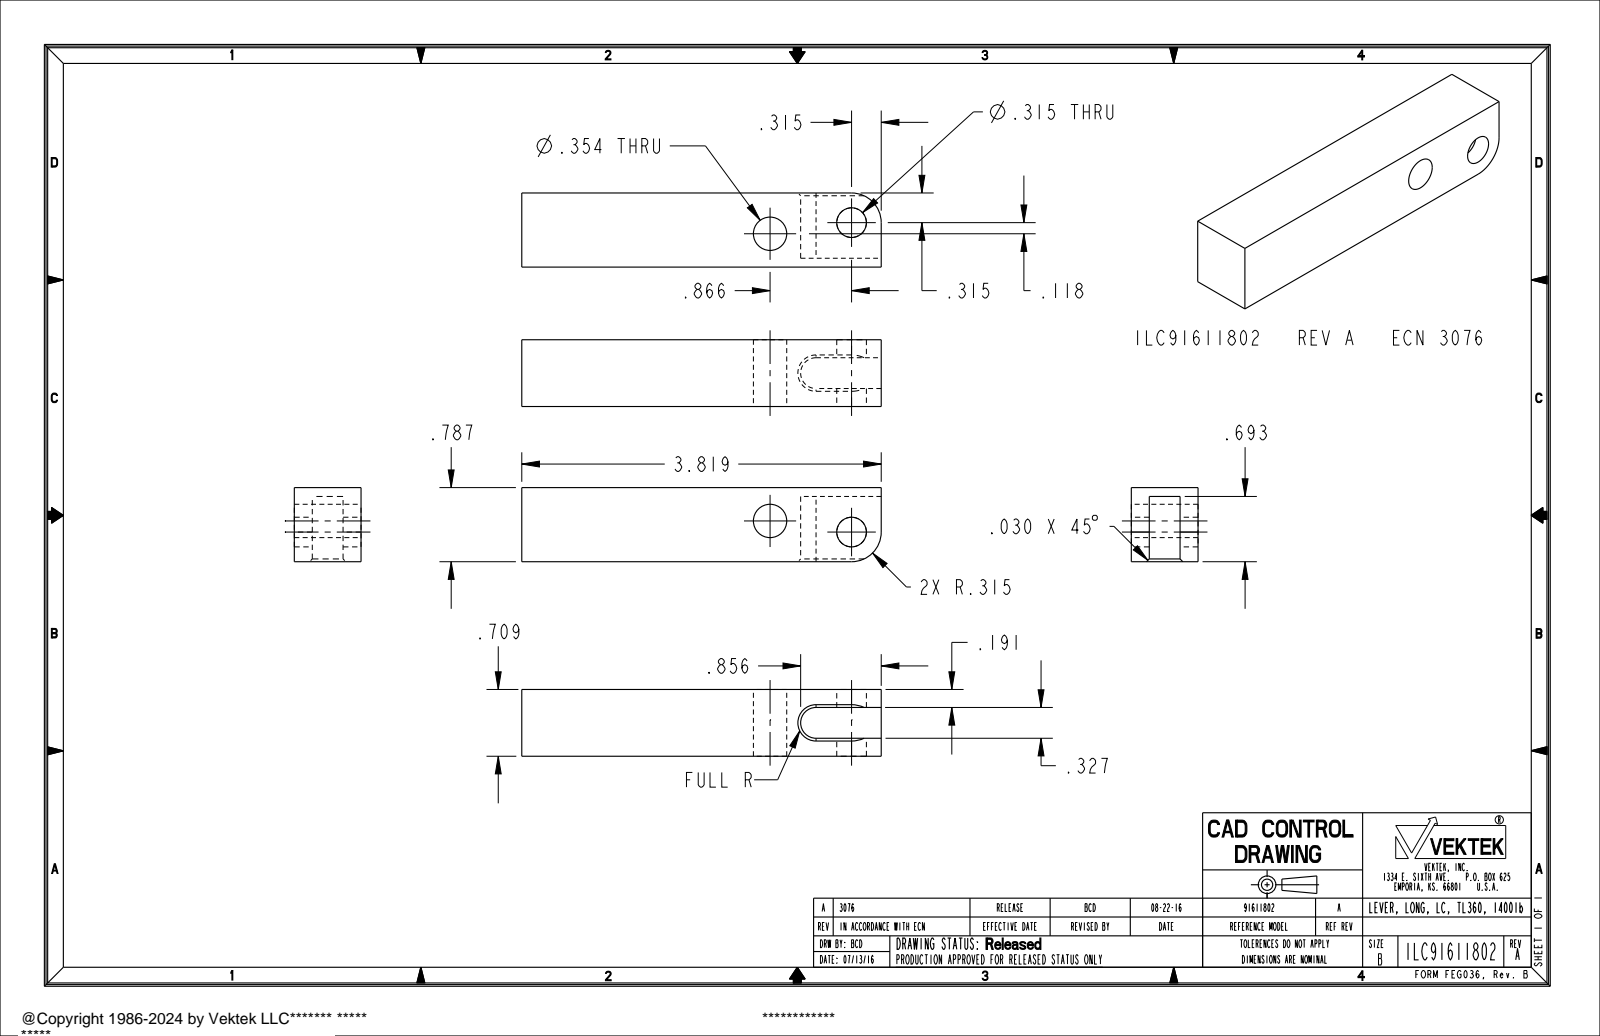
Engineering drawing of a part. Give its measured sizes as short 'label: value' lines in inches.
name: ILC91611802
written by: PRO/ENGINEER BY PARAMETRIC TECHNOLOGY CORPORATION, 2013320 (AUTOMOTIVE_DESIGN)
unit: in
bodies: 1 solid, 21 faces (11 planar, 9 cylindrical, 1 other)
size: 3.819 × 0.787 × 0.709
volume: 1.837 in³; area: 14.13 in²
holes: 1× ⌀0.315, 1× ⌀0.354
rounds: 1× R0.164, 1× R0.315
face distances: 0.709, 0.787, 0.191, 0.518, 0.327, 0.693, 0.094, 3.819
hole spacings: 0.874
